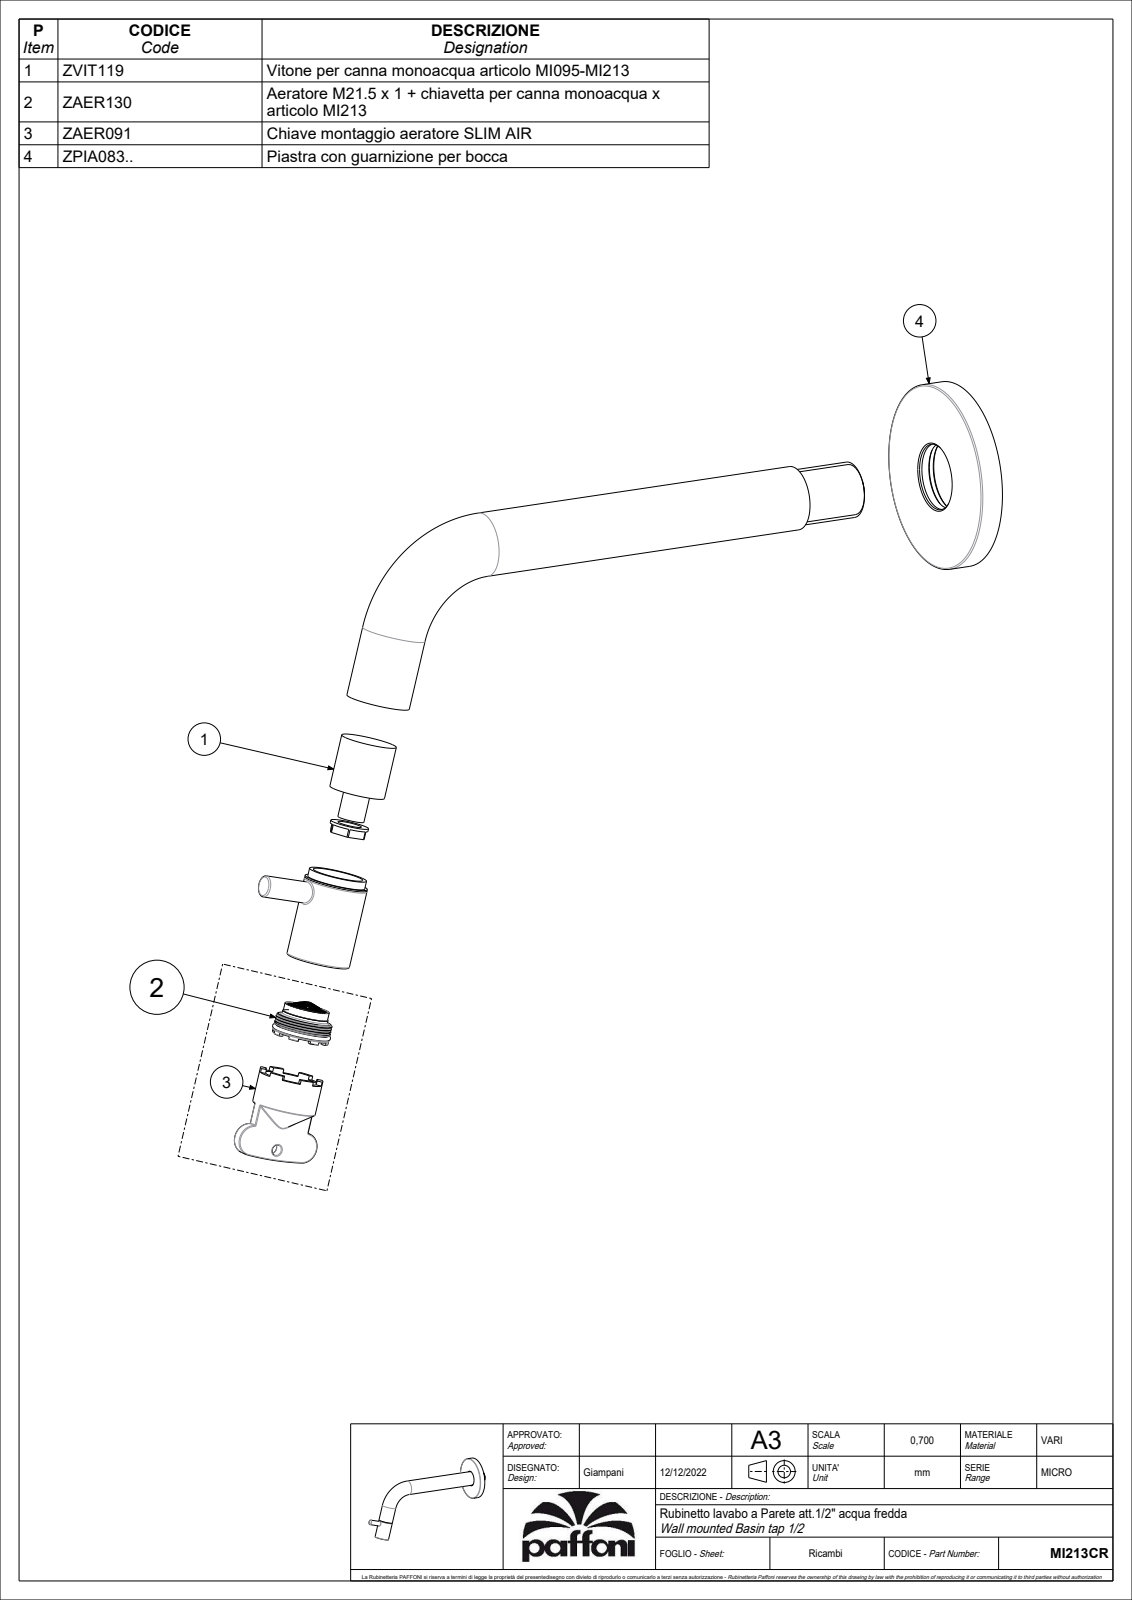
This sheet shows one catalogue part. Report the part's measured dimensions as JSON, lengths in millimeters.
{"part_name": "MI213CR", "step_written_by": "CREO PARAMETRIC BY PTC INC, 2020044 (CONFIG_CONTROL_DESIGN)", "units": "millimeters", "bodies": {"solids": 4, "faces": 3463, "planar": 3015, "cylindrical": 358, "other": 90}, "overall_size": [212.29, 122.45, 70], "volume_mm3": 65498, "surface_area_mm2": 49285, "round_holes": [[19, 3], [9, 2], [10.2, 1], [11, 1], [11.1, 1], [12.1, 1], [12.5, 1], [13.2, 1], [13.5, 1], [14, 1], [14.2, 1], [15, 1]], "round_bosses_or_shafts": [[0.8, 6], [24, 3], [70, 1], [33.8, 1], [23.9, 1], [21.4, 1], [21, 1], [19.25, 1]], "partial_cylinders_radius": [[0.12, 57], [10.69, 1]], "face_to_face_distances": [2, 7.5, 7, 9, 1.5, 0.5, 6, 5.5, 30.5, 23.8]}
